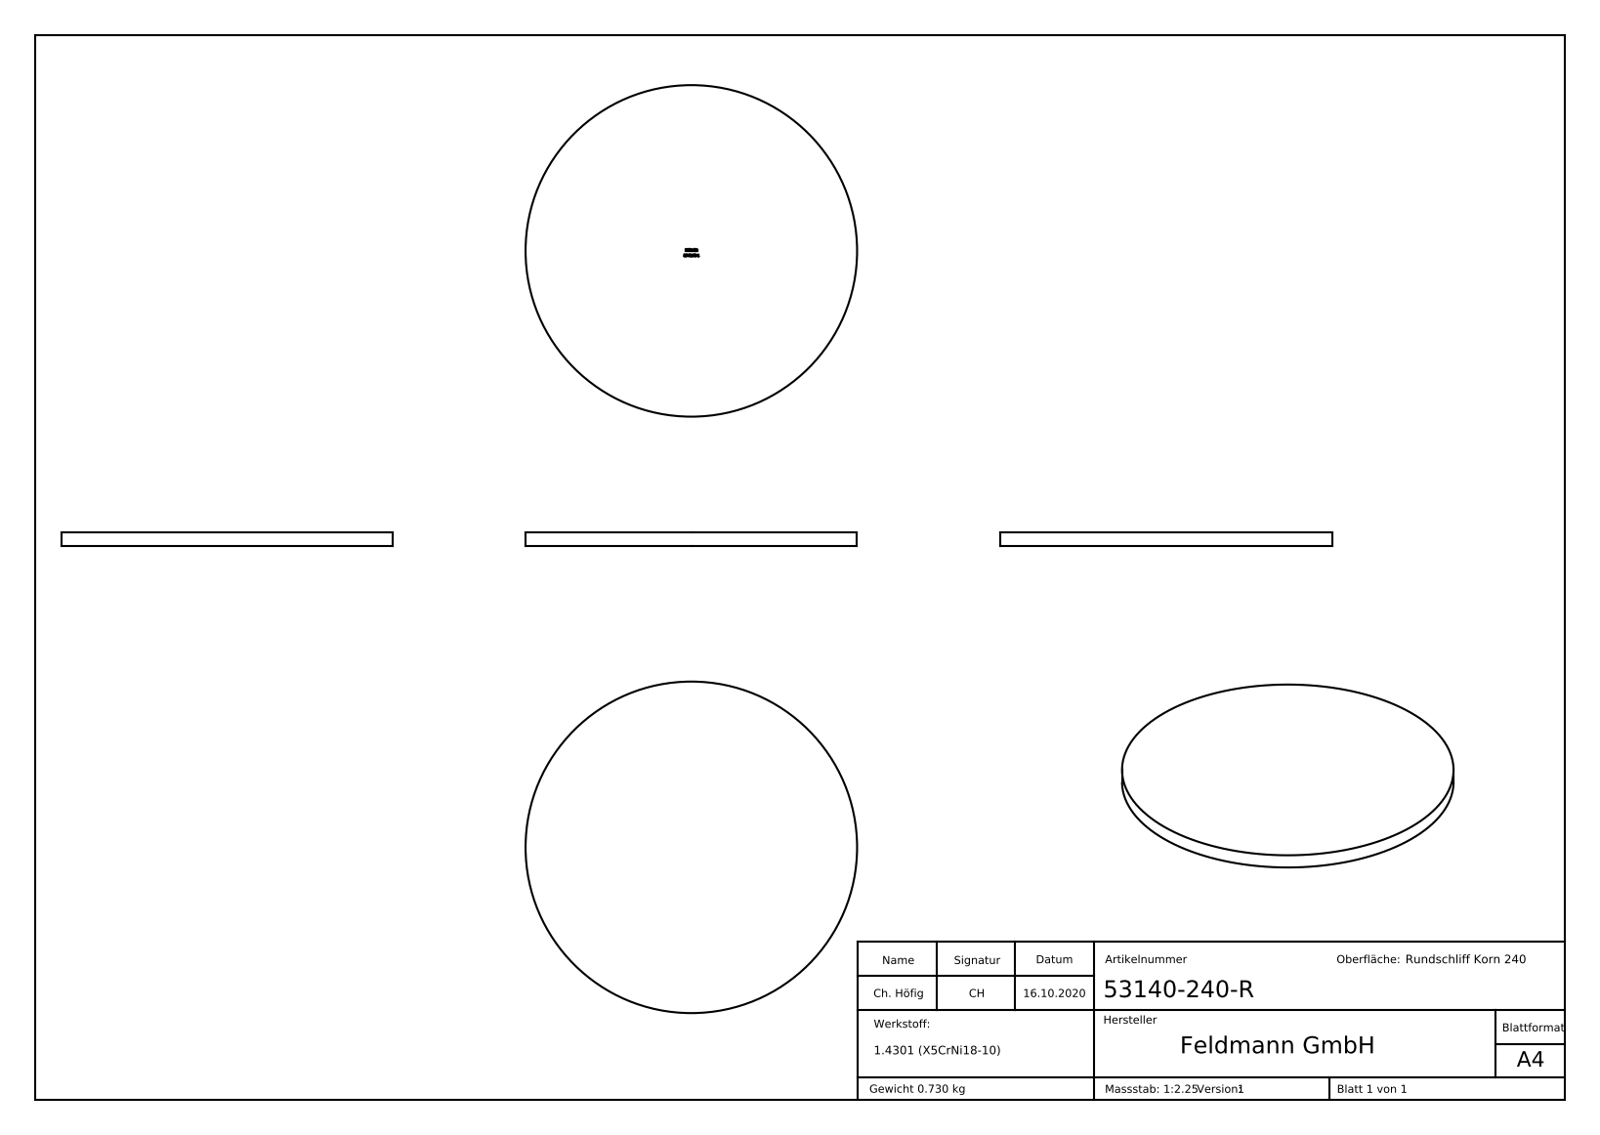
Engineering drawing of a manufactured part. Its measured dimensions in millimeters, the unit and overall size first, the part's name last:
Units: millimetres
Overall size (bounding box): 140 × 140 × 6
Round bosses / shafts (diameter × count): ⌀140 ×1
Main face-to-face distances: 6, 5.9, 1.21, 0.53, 1.28, 0.99, 2.32, 3.86, 0.92, 0.79
Volume: 92 363 mm³ · Surface area: 33 433 mm²
Bodies: 1 solid, 250 faces (149 planar, 2 cylindrical, 99 other)
Part name (STEP PRODUCT): 53140-240-R
STEP written by: SolidWorks 2018 (CONFIG_CONTROL_DESIGN)
